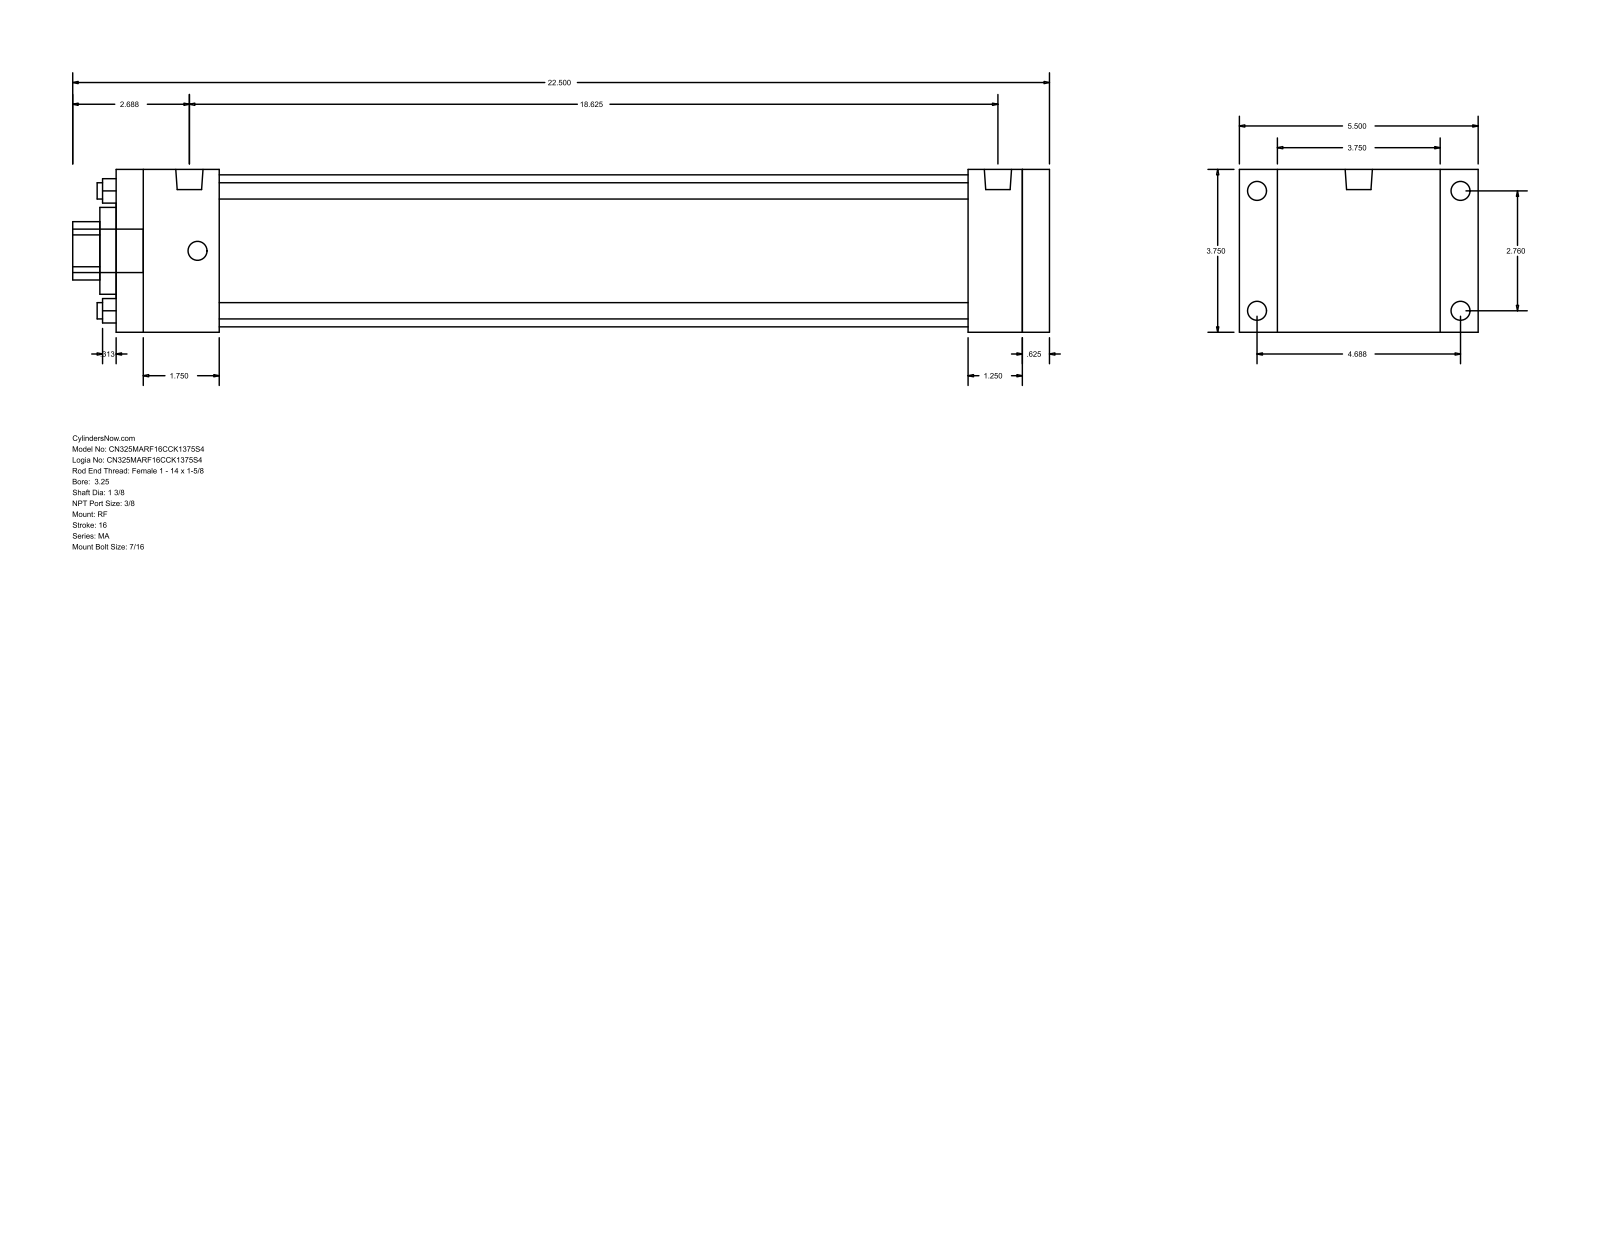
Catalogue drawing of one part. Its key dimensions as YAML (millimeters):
part_name: "MA_RF__0325_1.375"
step_written_by: "GSSL Pune (CONFIG_CONTROL_DESIGN)"
units: millimeters
bodies: {solids: 0, faces: 92, planar: 64, cylindrical: 28, other: 0}
overall_size: [571.5, 139.7, 95.25]
round_holes:
  - {diameter: 9.53, count: 4}
  - {diameter: 34.92, count: 1}
  - {diameter: 50.8, count: 1}
  - {diameter: 88.9, count: 1}
round_bosses_or_shafts:
  - {diameter: 11.11, count: 8}
  - {diameter: 15.93, count: 2}
  - {diameter: 25.4, count: 1}
partial_cylinders:
  - {radius: 17.06, count: 1}
face_to_face_distances: [95.24, 546.1, 15.88, 530.22, 22.23, 117.47, 498.48, 31.74, 47.62, 60.32]
hole_center_spacings: [49.57, 70.1, 99.14]
